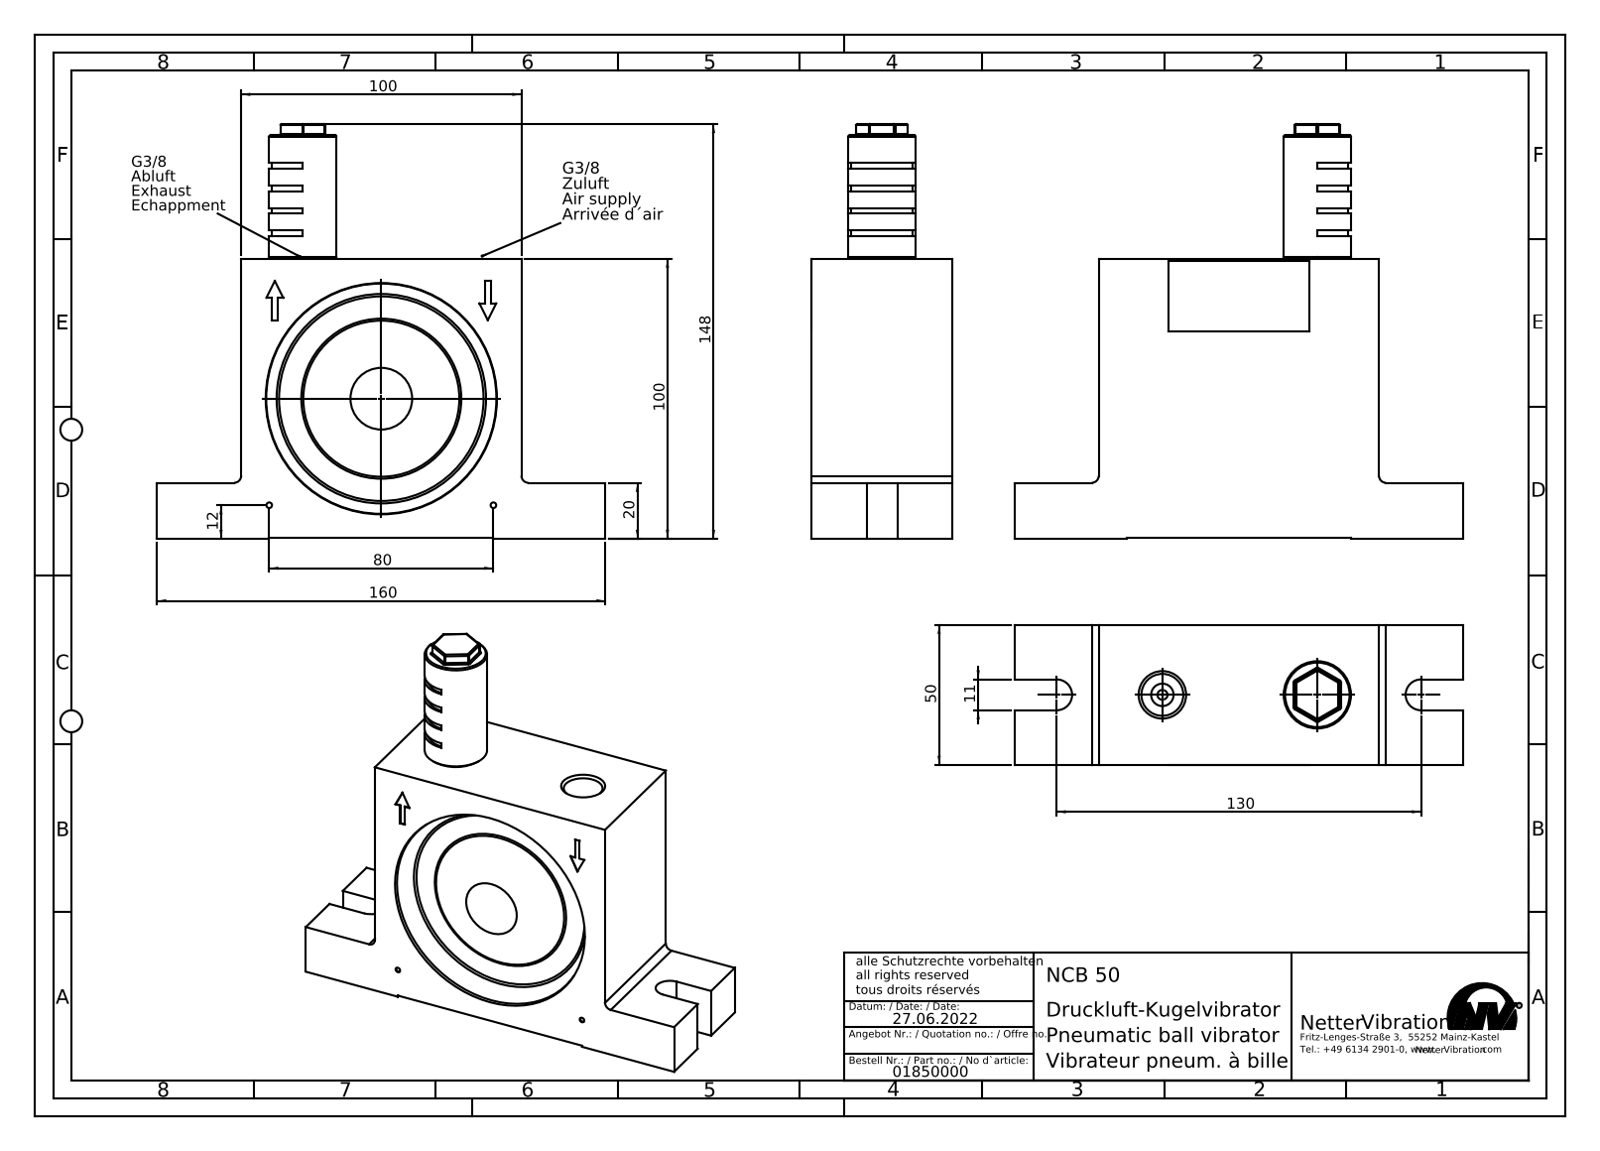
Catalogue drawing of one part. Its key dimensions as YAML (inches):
part_name: "NCB 50 Kugelvibrator #01850000"
step_written_by: "SolidWorks 2015 (AUTOMOTIVE_DESIGN)"
units: inches
bodies: {solids: 3, faces: 218, planar: 106, cylindrical: 47, other: 65}
overall_size: [6.299, 5.827, 1.978]
volume: 31.52
surface_area: 110.9
round_holes:
  - {diameter: 0.079, count: 2}
  - {diameter: 0.589, count: 2}
  - {diameter: 3.15, count: 1}
  - {diameter: 3.248, count: 1}
round_bosses_or_shafts:
  - {diameter: 0.945, count: 1}
  - {diameter: 0.656, count: 1}
partial_cylinders:
  - {radius: 0.02, count: 18}
  - {radius: 0.098, count: 2}
  - {radius: 0.217, count: 2}
  - {radius: 0.433, count: 1}
face_to_face_distances: [3.937, 1.969, 0.394, 1.575, 3.917, 0.02, 0.768, 0.787, 3.15, 1.683]
hole_center_spacings: [2.172, 2.177, 3.15]
